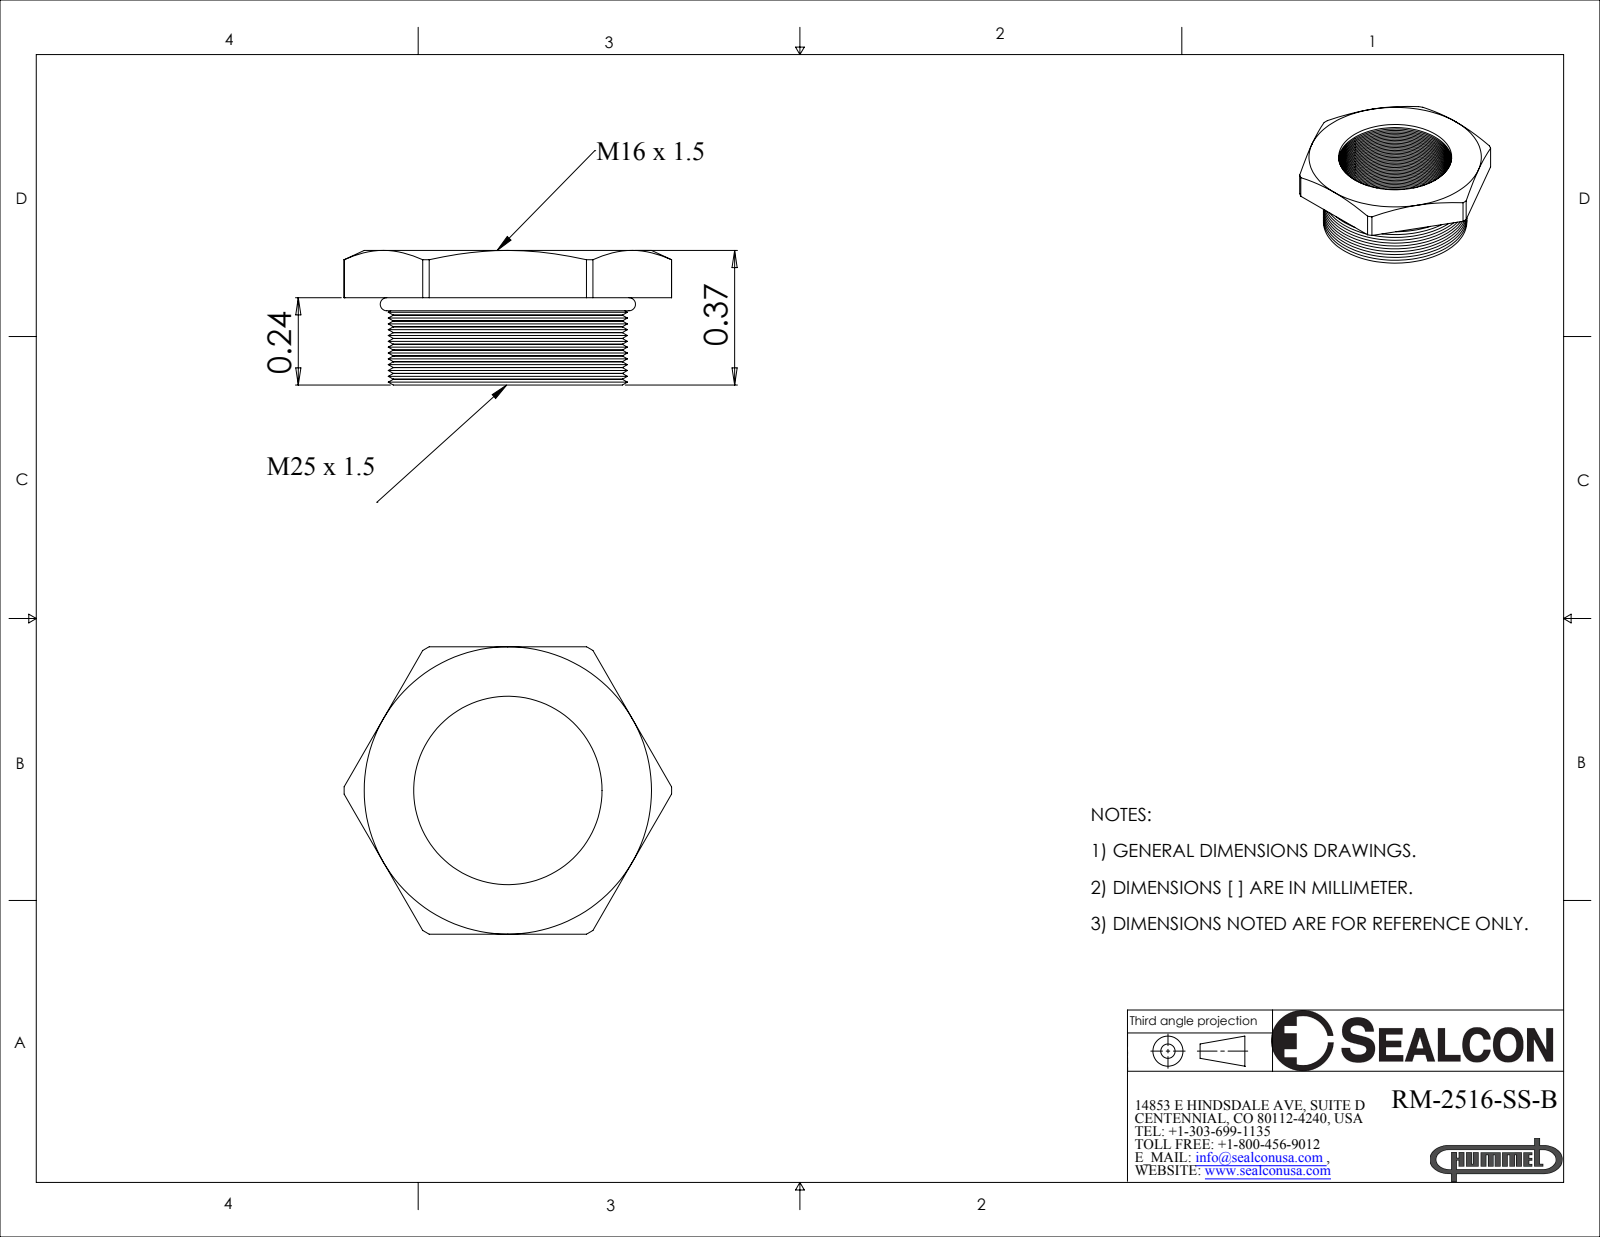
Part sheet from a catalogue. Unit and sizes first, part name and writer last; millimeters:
Units: millimetres
Overall size (bounding box): 22.9 × 20.1 × 9.4
Round holes (diameter × count): ⌀13.2 ×1
Round bosses / shafts (diameter × count): ⌀16 ×1
Partial cylindrical surfaces — rounded edges, fillets, slot ends (radius × count): R11.4 ×1
Main face-to-face distances: 3.3, 20.1, 6.1, 9.4
Volume: 1 100 mm³ · Surface area: 2 152 mm²
Bodies: 2 solids, 245 faces (9 planar, 81 cylindrical, 155 other)
Part name (STEP PRODUCT): RM-2516-SS-B
STEP written by: SolidWorks 2008 (CONFIG_CONTROL_DESIGN)
